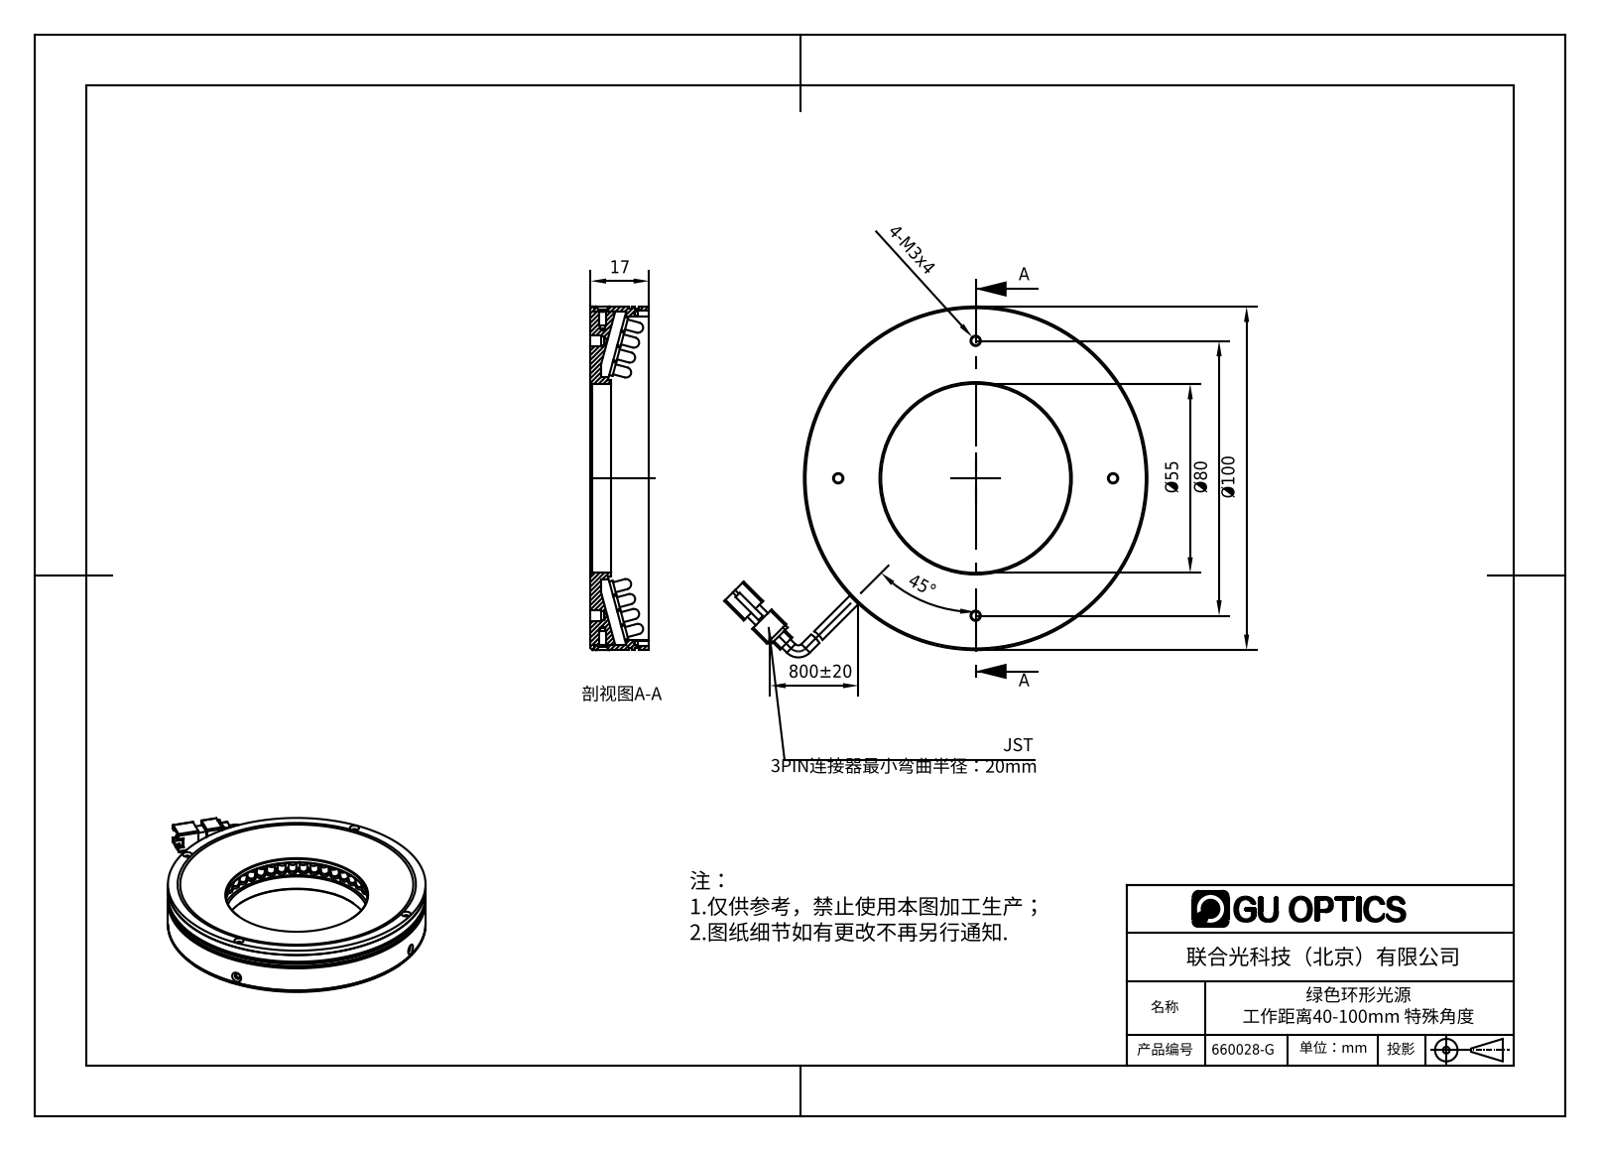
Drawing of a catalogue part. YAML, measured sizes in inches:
part_name: "660028-G"
step_written_by: "SolidWorks 2016 (AUTOMOTIVE_DESIGN)"
units: inches
bodies: {solids: 216, faces: 3870, planar: 2609, cylindrical: 980, other: 281}
overall_size: [4.85, 4.021, 0.884]
volume: 3.55
surface_area: 106.7
round_holes:
  - {diameter: 0.063, count: 6}
  - {diameter: 0.049, count: 4}
  - {diameter: 0.067, count: 4}
  - {diameter: 0.098, count: 4}
  - {diameter: 0.118, count: 4}
  - {diameter: 0.138, count: 4}
  - {diameter: 0.079, count: 2}
  - {diameter: 0.094, count: 2}
  - {diameter: 2.165, count: 1}
  - {diameter: 3.701, count: 1}
round_bosses_or_shafts:
  - {diameter: 0.15, count: 210}
  - {diameter: 0.118, count: 210}
  - {diameter: 0.138, count: 2}
  - {diameter: 3.937, count: 1}
  - {diameter: 3.898, count: 1}
  - {diameter: 3.819, count: 1}
  - {diameter: 2.323, count: 1}
  - {diameter: 2.244, count: 1}
partial_cylinders:
  - {radius: 0.02, count: 10}
  - {radius: 0.039, count: 4}
  - {radius: 0.065, count: 1}
  - {radius: 0.295, count: 1}
face_to_face_distances: [0.039, 0.079, 0.669, 0.118, 0.63, 0.02, 0.748, 0.551, 0.709, 0.197]
hole_center_spacings: [2.46, 0.315, 1.575, 1.89, 2.227, 2.672, 3.465, 3.15]
